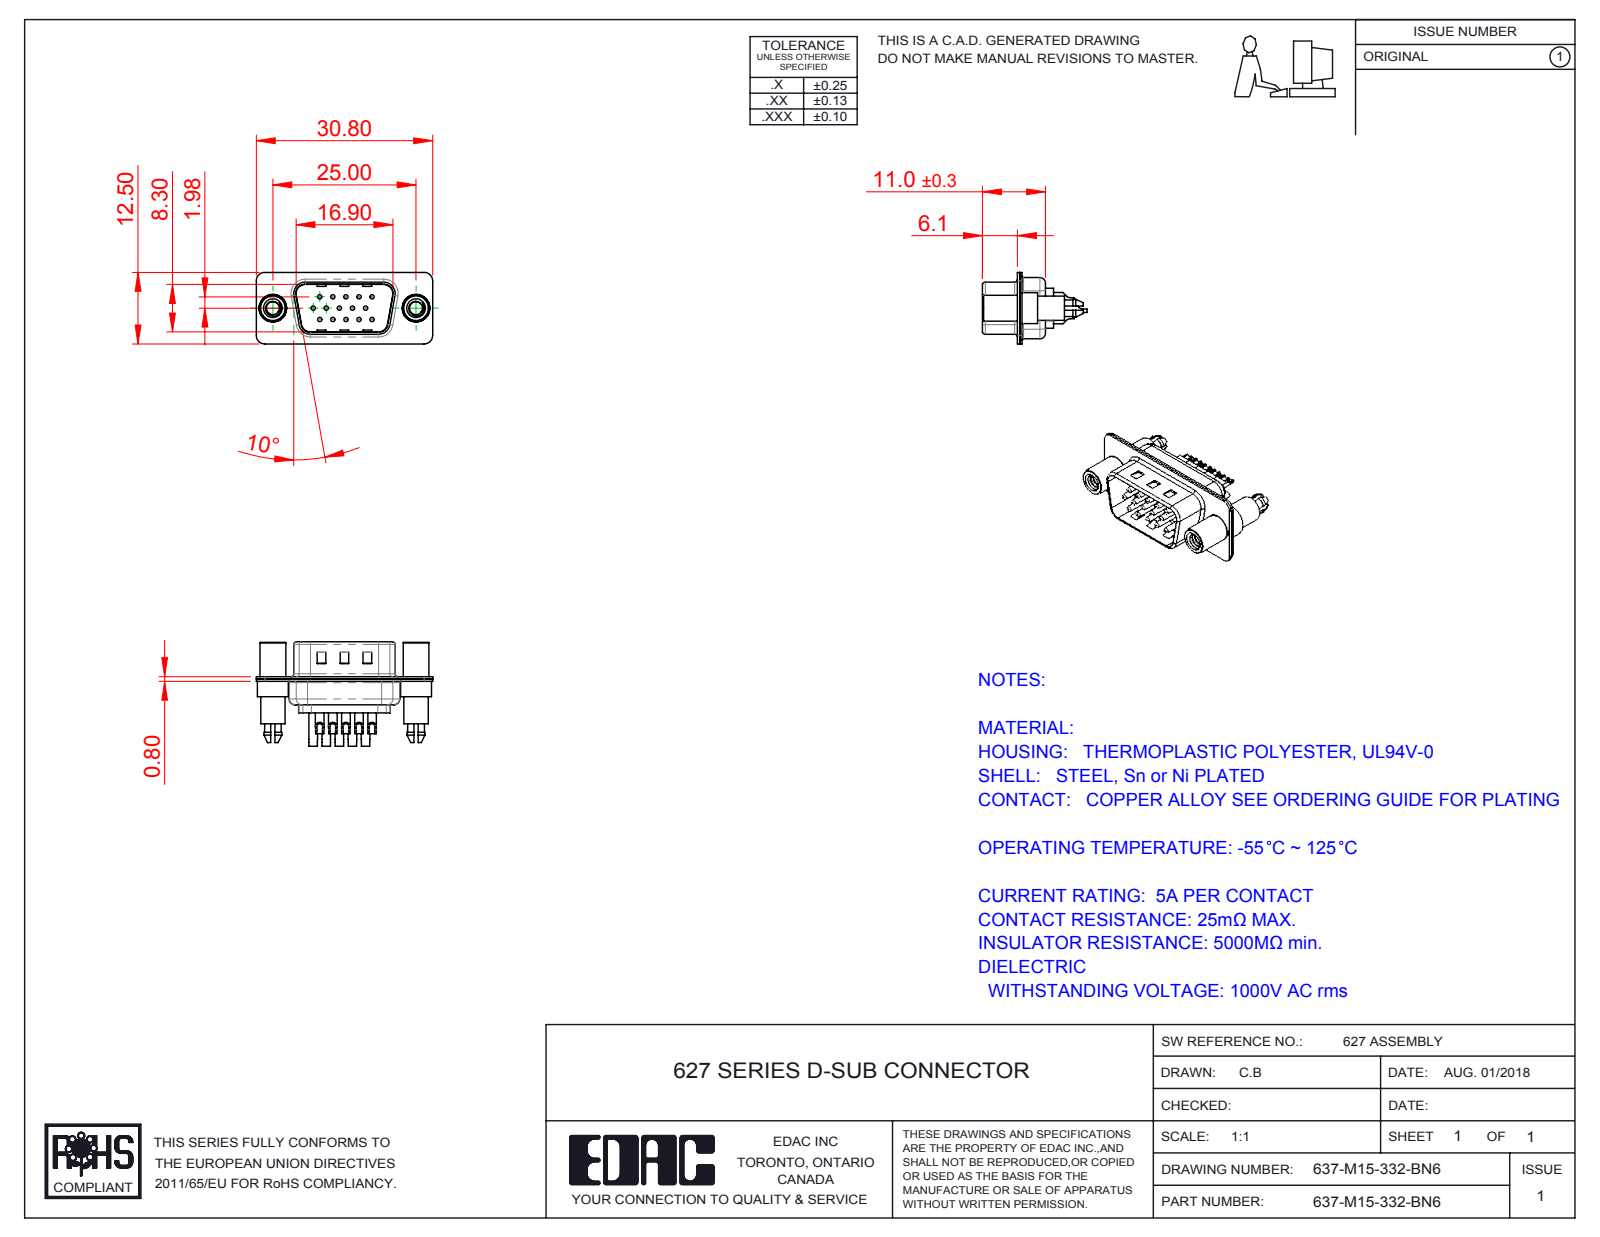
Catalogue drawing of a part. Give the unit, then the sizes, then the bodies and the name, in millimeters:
Units: millimetres
Overall size (bounding box): 30.8 × 18.25 × 12.5
Round holes (diameter × count): ⌀0.75 ×15, ⌀1 ×15, ⌀1.6 ×15, ⌀2 ×15, ⌀2.26 ×2, ⌀4 ×2, ⌀4.8 ×2
Round bosses / shafts (diameter × count): ⌀1.5 ×15, ⌀5.4 ×2, ⌀4.9 ×2, ⌀4.5 ×2, ⌀4.25 ×2
Partial cylindrical surfaces — rounded edges, fillets, slot ends (radius × count): R1.5 ×18, R2 ×12, R1.6 ×10, R0.5 ×8, R1 ×7, R0.25 ×4, R0.6 ×4, R0.65 ×4
Main face-to-face distances: 0.4, 0.8, 9.5, 9.1, 0.65, 8.7, 9.9, 0.75, 1.4, 6.3
Hole centre spacings: 3.96, 2.28, 2.29, 4.57, 6.05, 6.86, 7.92, 6.04
Volume: 1 735 mm³ · Surface area: 4 760 mm²
Bodies: 20 solids, 943 faces (280 planar, 405 cylindrical, 258 other)
Part name (STEP PRODUCT): 637M Contact Row 2_32; 637M 4-40 Threaded Standoff and Boardlock; 637M Contact Row 3_32; 637M Contact Row 1_32 (+4 more)
STEP written by: SolidWorks 2016 (CONFIG_CONTROL_DESIGN)
